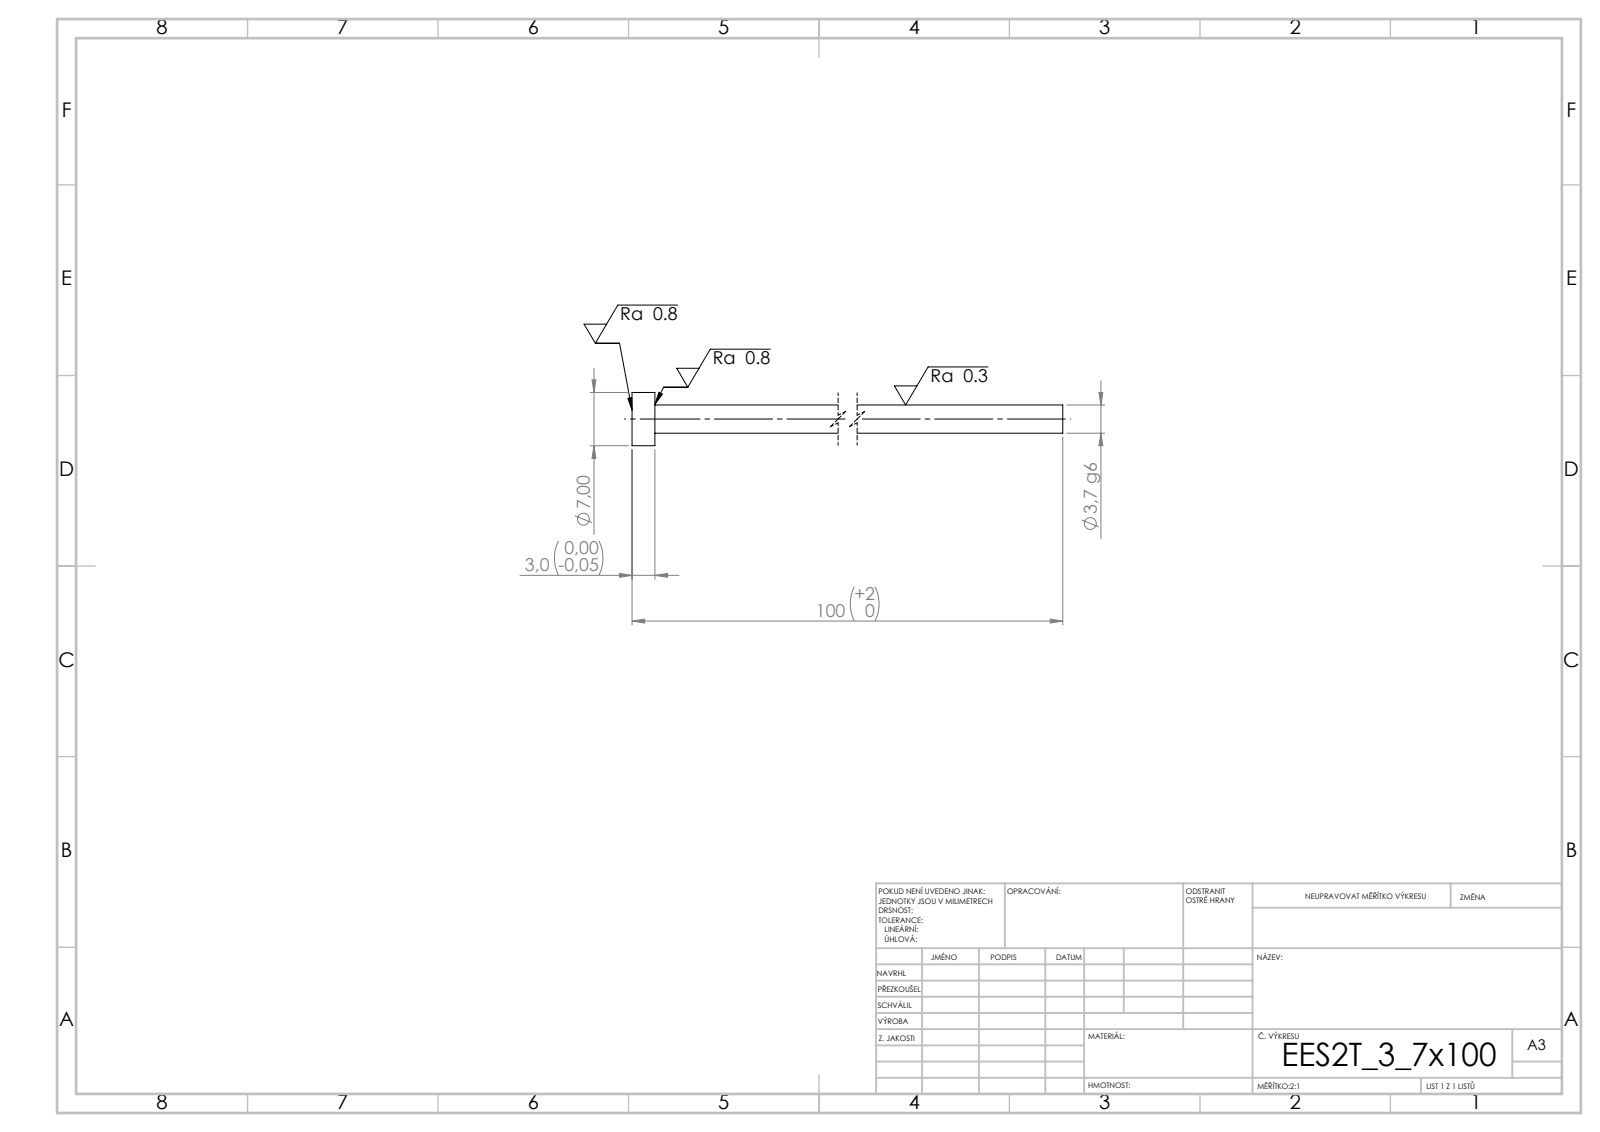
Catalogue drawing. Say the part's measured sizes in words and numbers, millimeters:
Its 3-D file was written by "SolidWorks 2019 (CONFIG_CONTROL_DESIGN)". It is 1 solid with 7 faces: 3 planar, 4 cylindrical and 0 other. Overall it measures 100 by 7 by 7 millimeters. Its volume is 1 158 cubic millimeters and its surface area 1 270 square millimeters. Round bosses or shafts: 1 of diameter 7, 1 of diameter 3.7. The main face-to-face distances are 3, 100, 97.
